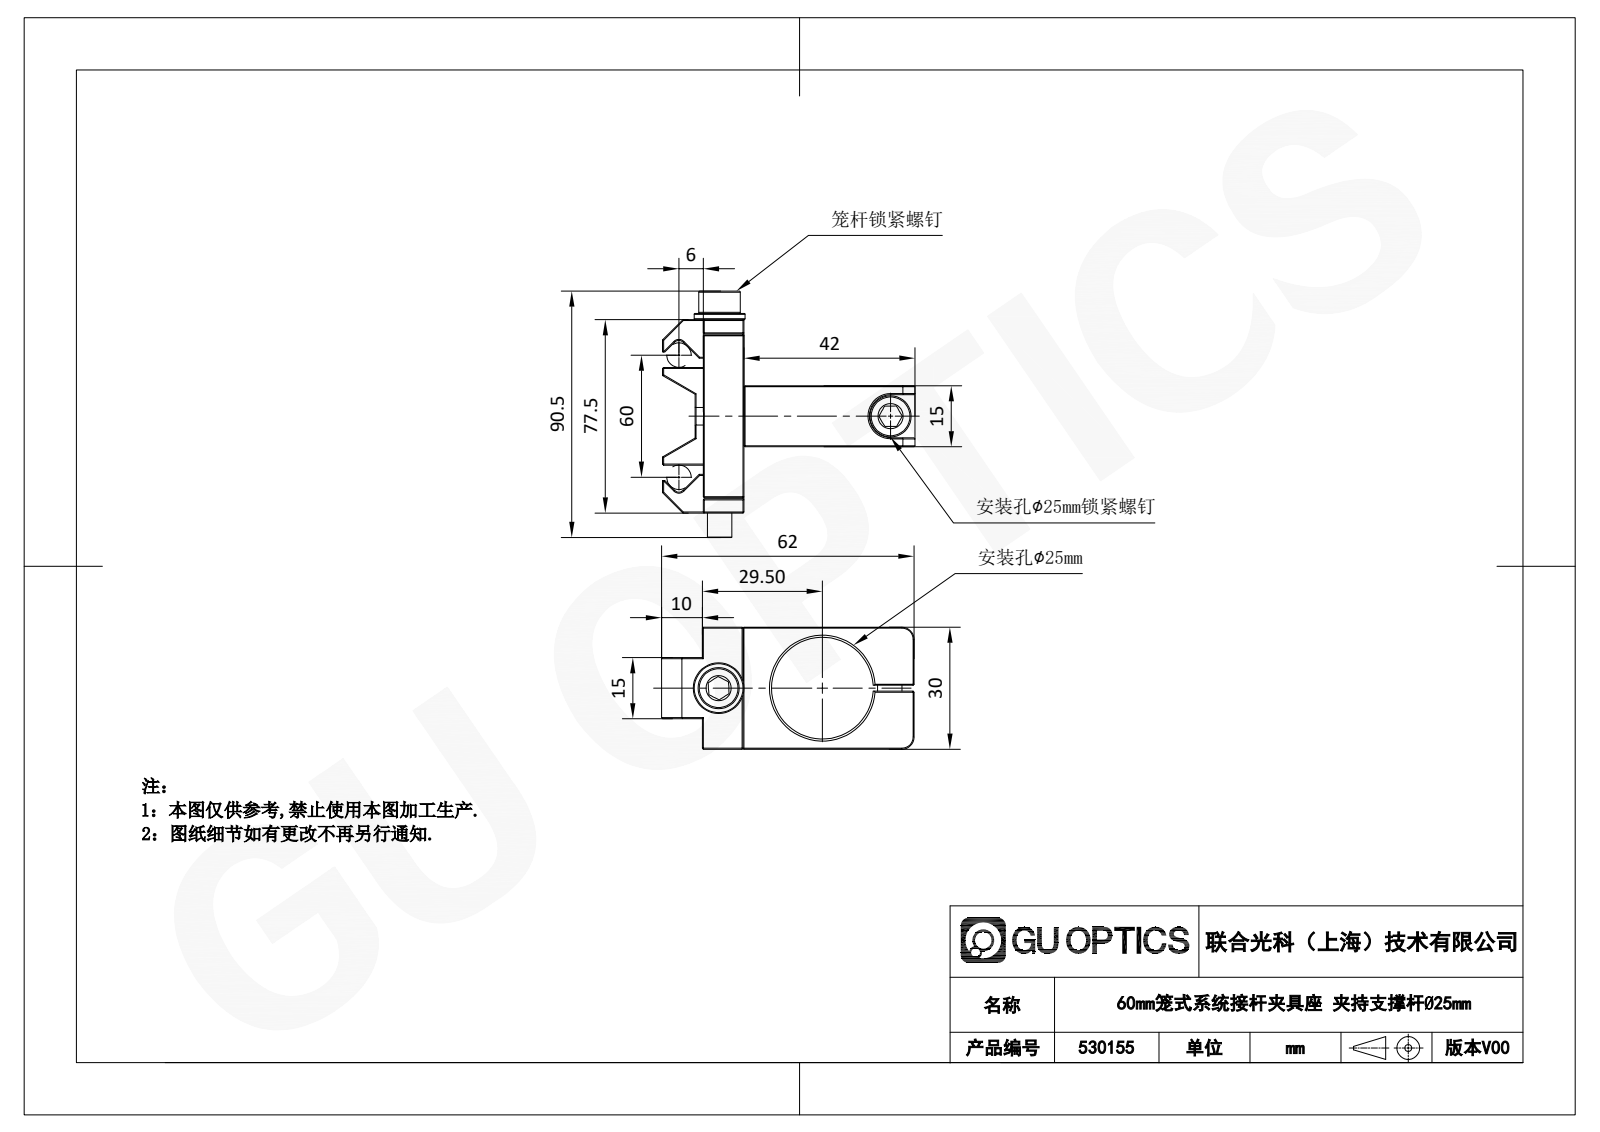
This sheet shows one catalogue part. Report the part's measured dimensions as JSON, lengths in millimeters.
{"part_name": "530155", "step_written_by": "SolidWorks 2020 (CONFIG_CONTROL_DESIGN)", "units": "millimeters", "bodies": {"solids": 9, "faces": 356, "planar": 278, "cylindrical": 28, "other": 50}, "overall_size": [90.5, 62, 30], "volume_mm3": 38910, "surface_area_mm2": 20525, "round_holes": [[3.3, 2], [4.5, 2], [5, 2], [7.8, 2], [6.2, 1], [6.4, 1], [6.6, 1], [25, 1]], "round_bosses_or_shafts": [[10.2, 2], [7.2, 2], [6, 2], [4, 2], [12.5, 1]], "partial_cylinders_radius": [[1.5, 2], [3, 2], [5.3, 1]], "face_to_face_distances": [30, 10, 15, 7.5, 22.5, 2, 31.24, 46.24, 6, 12], "hole_center_spacings": [21.5, 25.5]}
